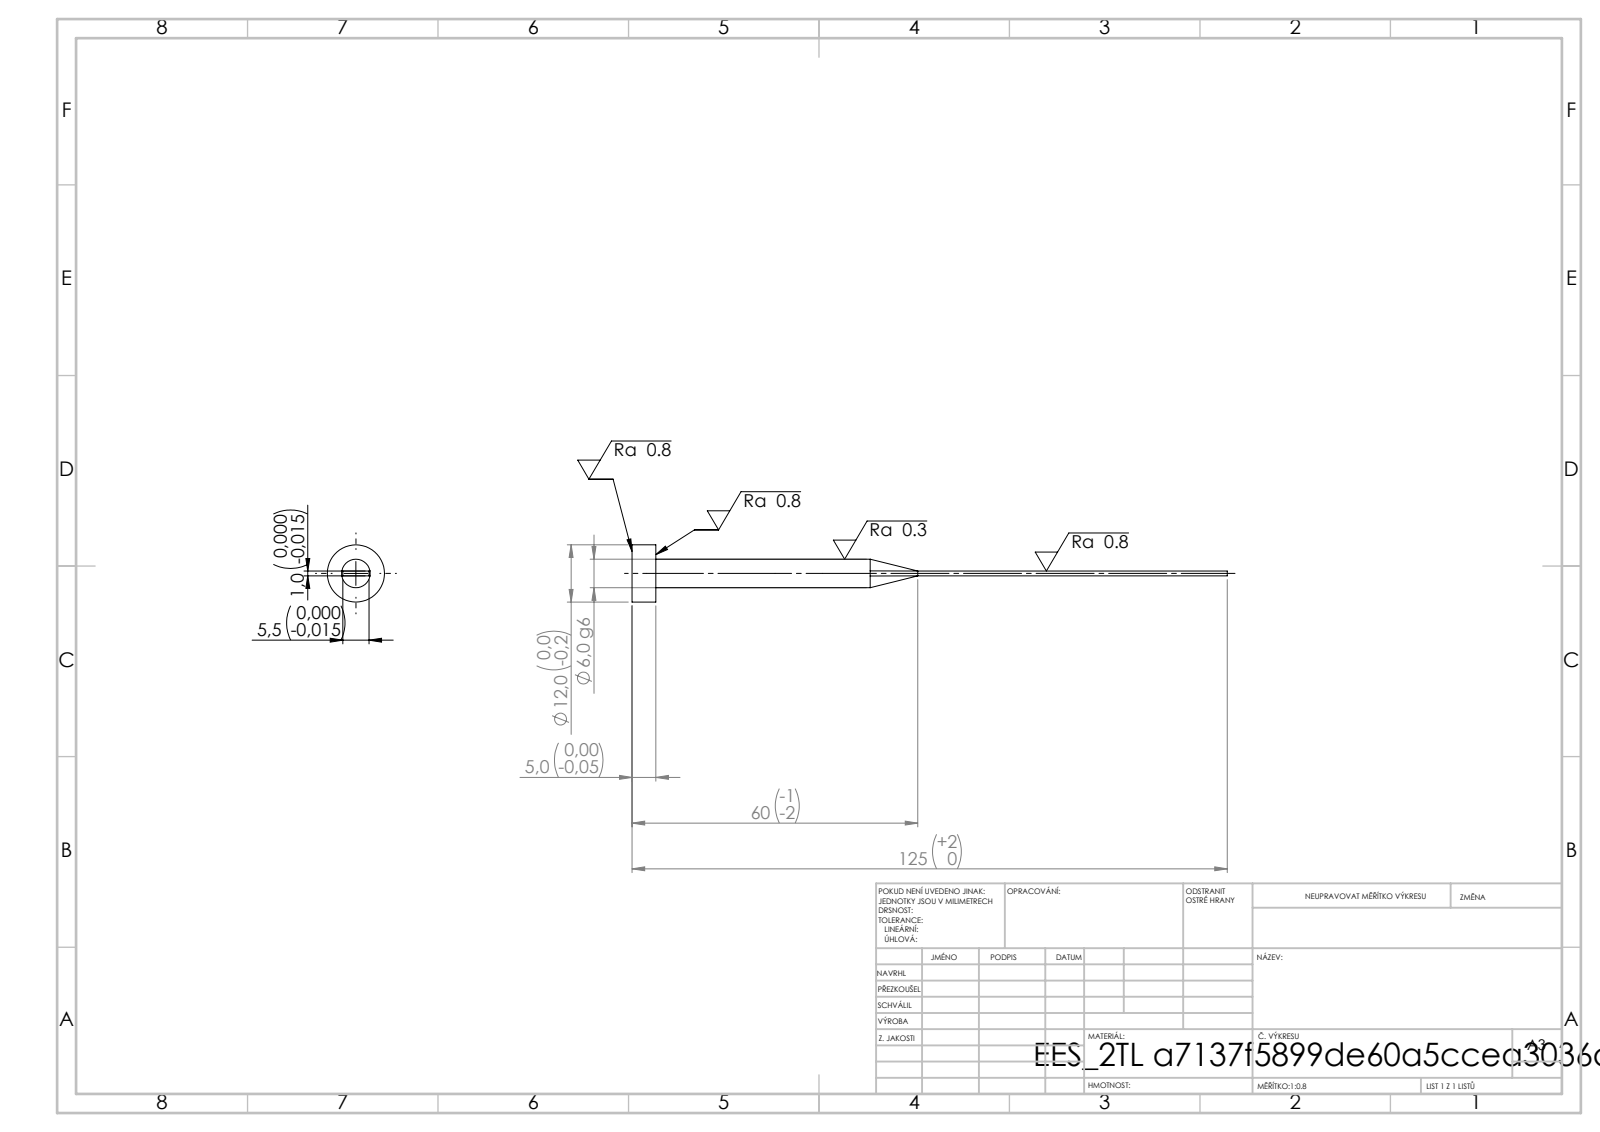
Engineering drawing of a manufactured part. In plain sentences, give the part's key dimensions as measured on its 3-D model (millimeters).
Its 3-D file was written by "SolidWorks 2019 (CONFIG_CONTROL_DESIGN)". It is 1 solid with 15 faces: 7 planar, 4 cylindrical and 4 other. Overall it measures 125 by 12 by 12 millimeters. Its volume is 2 355 cubic millimeters and its surface area 2 239 square millimeters. Round bosses or shafts: 1 of diameter 12, 1 of diameter 6. The main face-to-face distances are 1, 5, 5.5, 125, 120.
